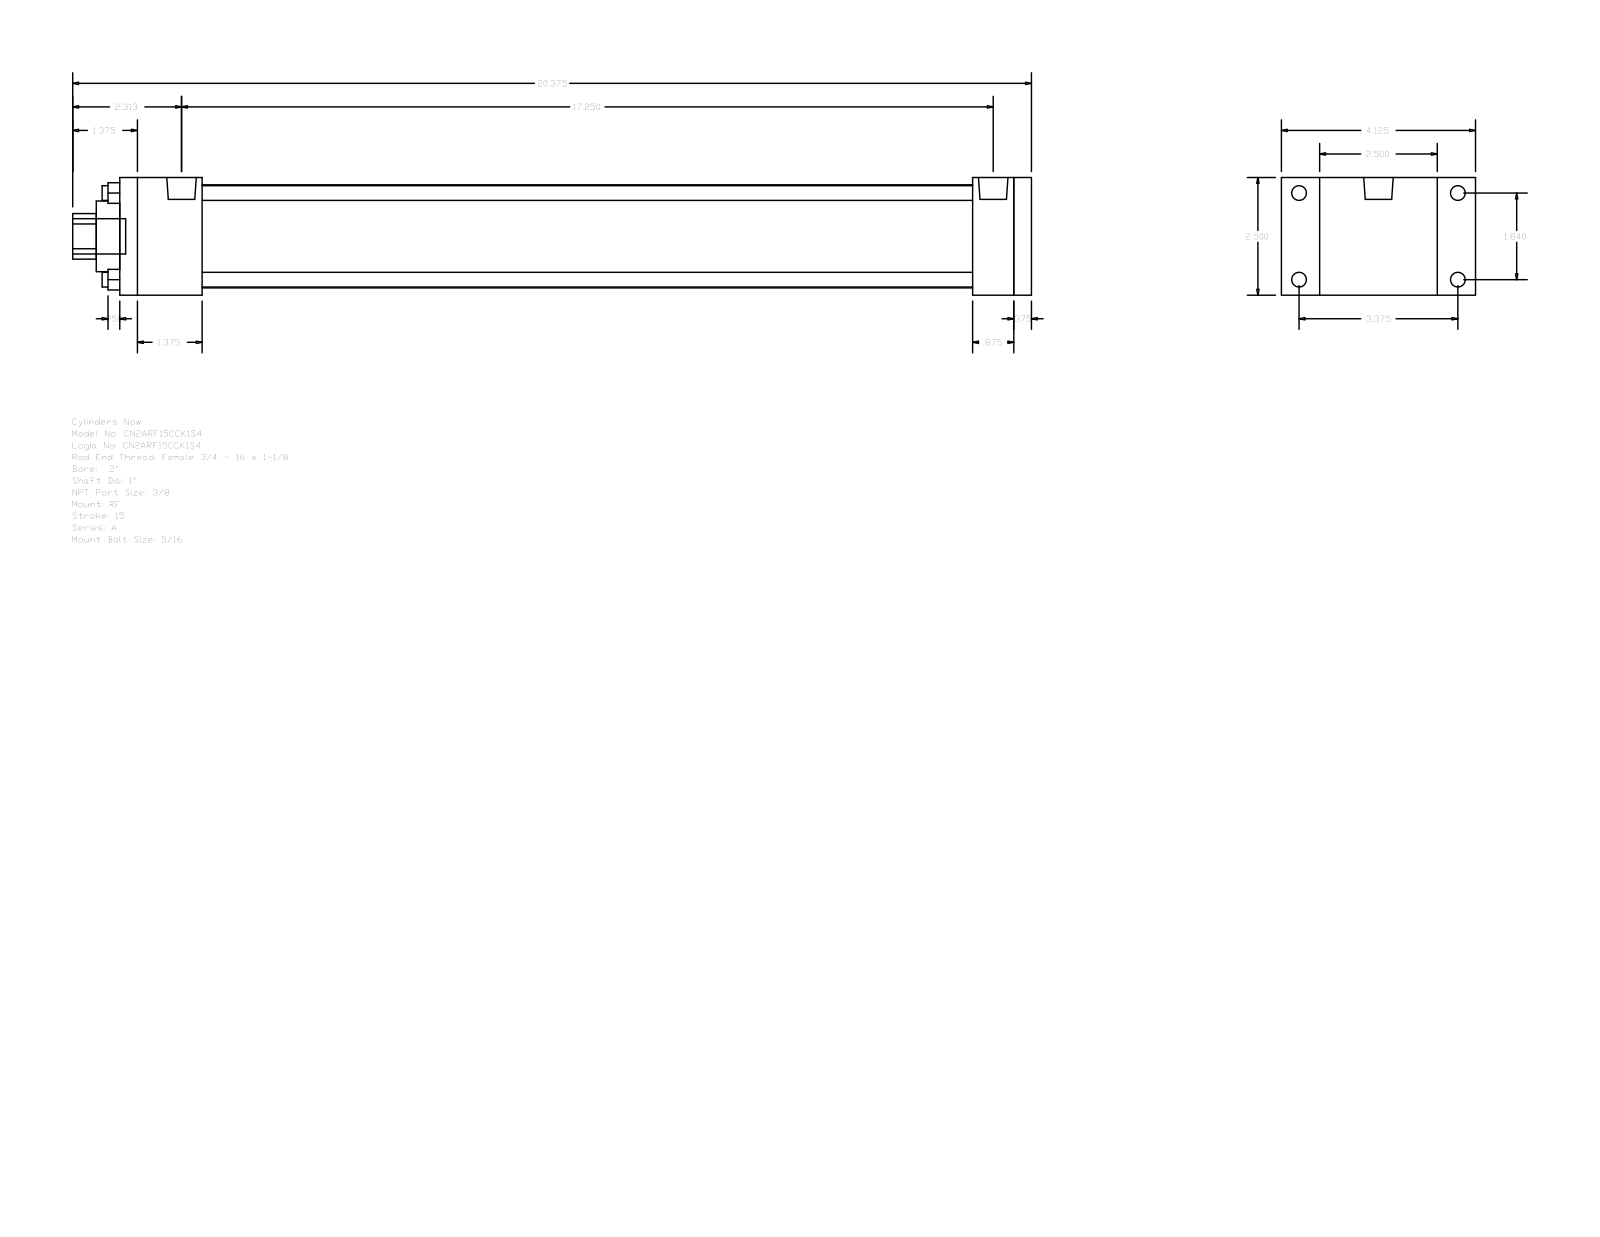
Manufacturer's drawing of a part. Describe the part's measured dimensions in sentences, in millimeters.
The part is named "A_RF__0200_1". Its 3-D file was written by "GSSL Pune (CONFIG_CONTROL_DESIGN)". It is 0 solids with 92 faces: 64 planar, 28 cylindrical and 0 other. Overall it measures 517.52 by 104.78 by 63.5 millimeters. Round holes: 4 of diameter 7.94, 1 of diameter 25.4, 1 of diameter 38.1, 1 of diameter 55.63. Round bosses or shafts: 4 of diameter 7.94, 4 of diameter 5.56, 2 of diameter 15.93, 1 of diameter 19.05. Partial cylindrical surfaces (rounded edges, fillets, slot ends): 1 of radius 12.29. The main face-to-face distances are 63.5, 9.52, 492.12, 482.6, 20.64, 44.45, 438.15, 447.67, 460.37, 415.92. The hole center spacings are 33.05, 46.74, 66.1.
